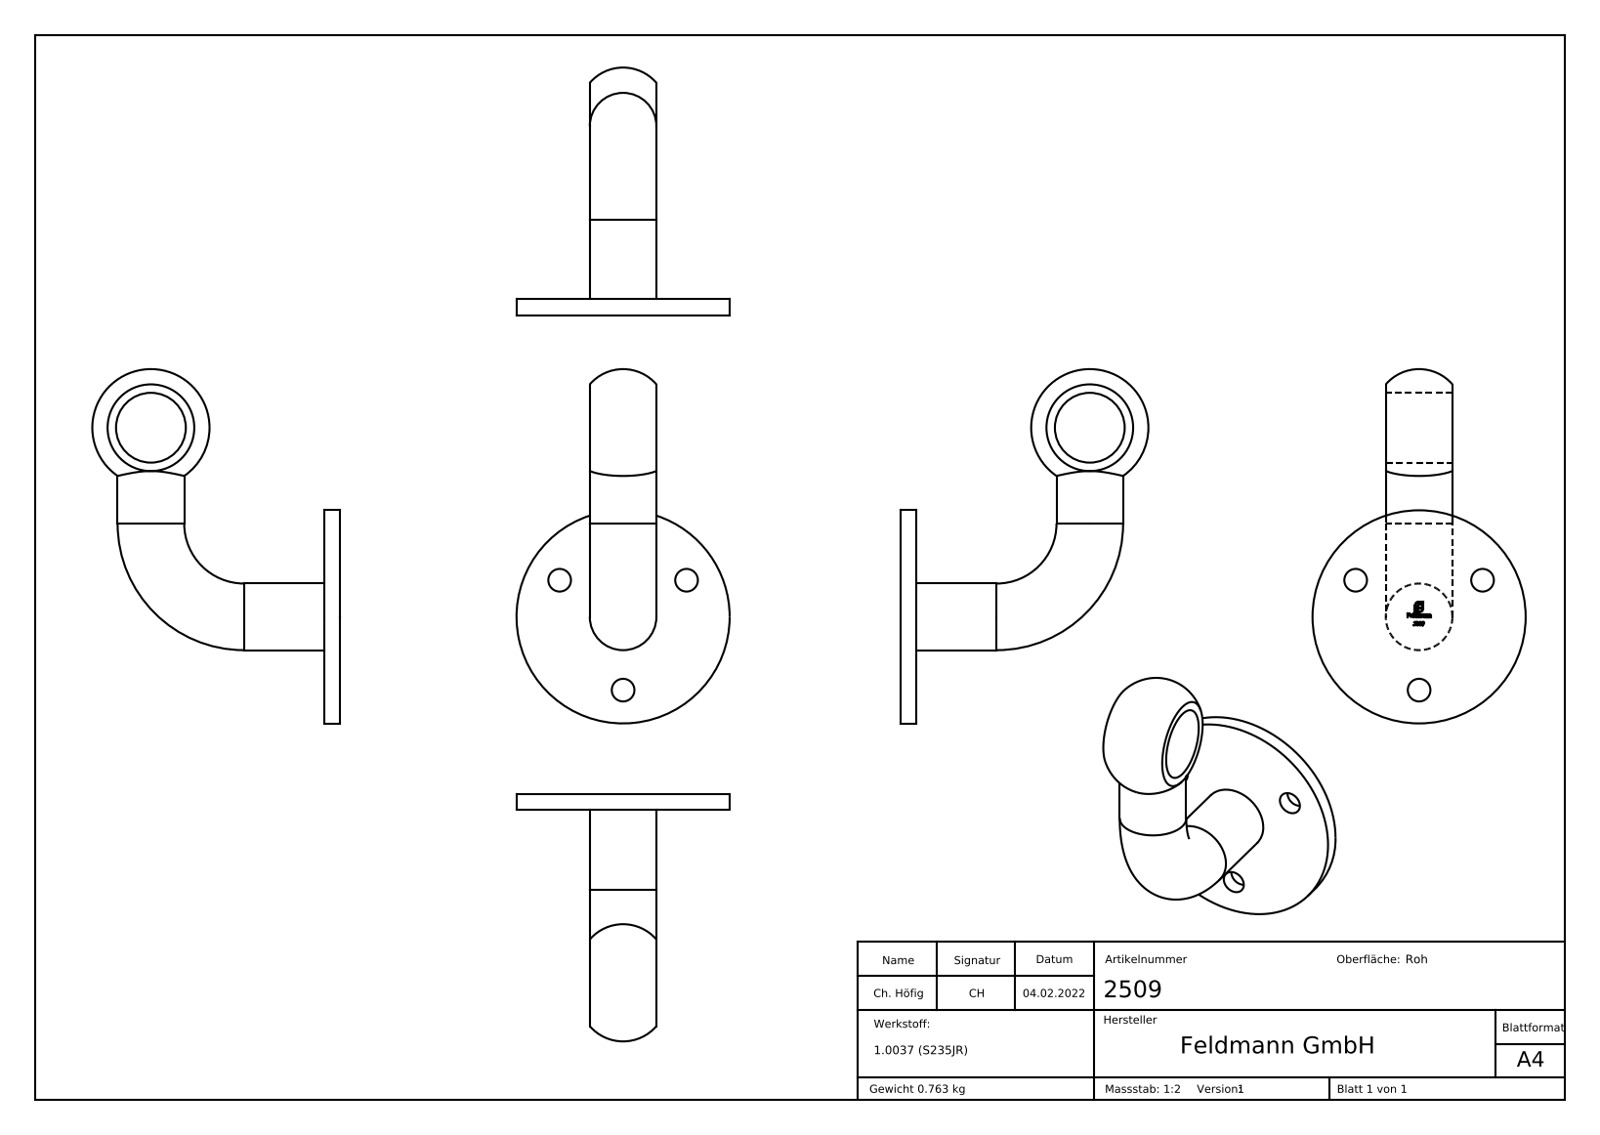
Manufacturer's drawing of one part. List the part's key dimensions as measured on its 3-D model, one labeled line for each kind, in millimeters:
Part name (STEP PRODUCT): 2509
STEP written by: SolidWorks 2018 (CONFIG_CONTROL_DESIGN)
Units: millimetres
Bodies: 1 solid, 232 faces (113 planar, 14 cylindrical, 105 other)
Overall size (bounding box): 133 × 93 × 80
Volume: 97 761 mm³ · Surface area: 25 019 mm²
Round holes (diameter × count): ⌀8.5 ×3, ⌀26.2 ×1
Round bosses / shafts (diameter × count): ⌀25 ×2, ⌀80 ×1
Main face-to-face distances: 6, 25, 5.9, 0.31, 0.87, 2.49, 0.39, 3.36, 0.41, 0.32
Hole centre spacings: 47.63, 47.64
